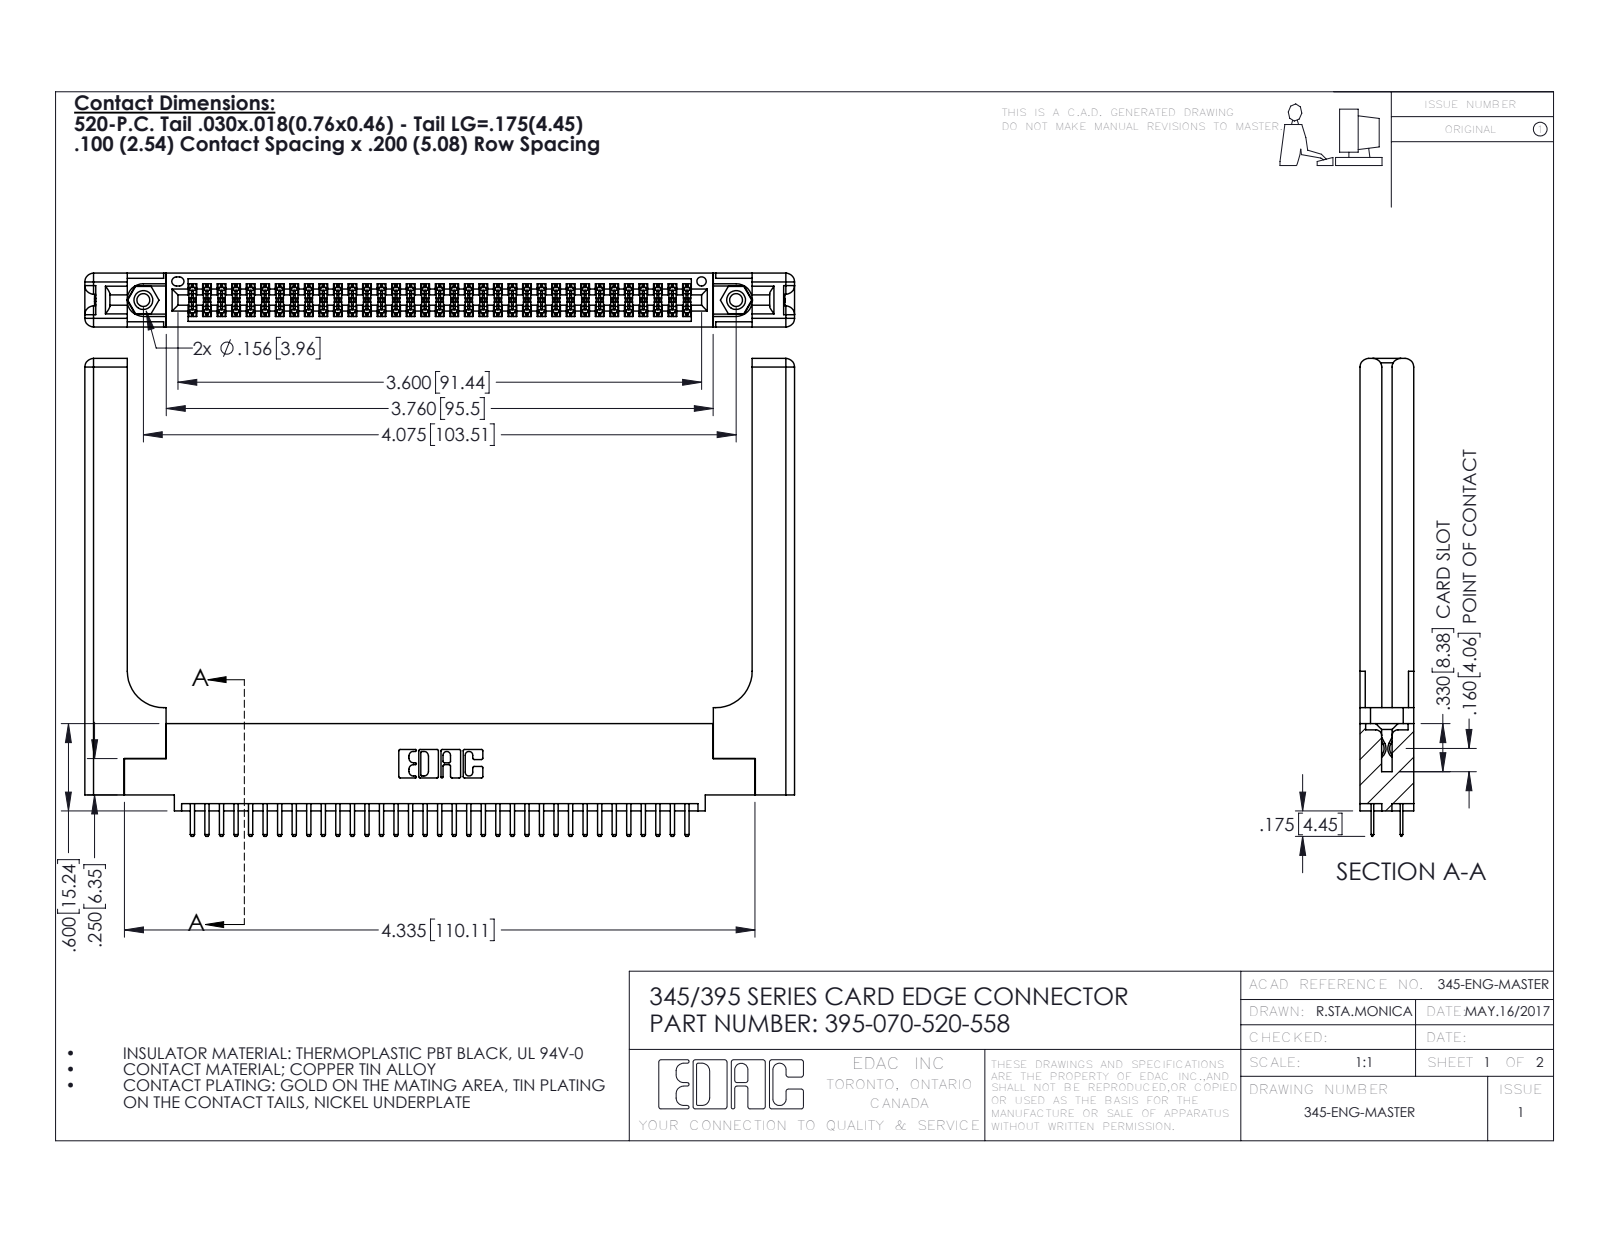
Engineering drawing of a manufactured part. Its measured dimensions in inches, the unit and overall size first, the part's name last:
Units: inches
Overall size (bounding box): 4.879 × 3.285 × 0.37
Round holes (diameter × count): ⌀0.089 ×2, ⌀0.125 ×2, ⌀0.156 ×2, ⌀0.064 ×1
Round bosses / shafts (diameter × count): ⌀0.155 ×2
Partial cylindrical surfaces — rounded edges, fillets, slot ends (radius × count): R0.006 ×105, R0.01 ×74, R0.01 ×22, R0.06 ×16, R0.007 ×6, R0.031 ×6, R0.026 ×3, R0.014 ×2
Main face-to-face distances: 0.37, 0.072, 0.298, 0.2, 0.098, 0.272, 0.025, 0.225, 0.148, 0.15
Hole centre spacings: 0.27, 3.839, 4.075
Volume: 1.241 in³ · Surface area: 34.87 in²
Bodies: 75 solids, 4166 faces (2682 planar, 1424 cylindrical, 60 other)
Part name (STEP PRODUCT): 395-070-520-558; 345 Part_0.110 Offset - 0.156 Dia-TH; 345-292-001_345-293-120; 345-250-001_345-250-001-102 (+1 more)
STEP written by: SolidWorks 2016 (CONFIG_CONTROL_DESIGN)
